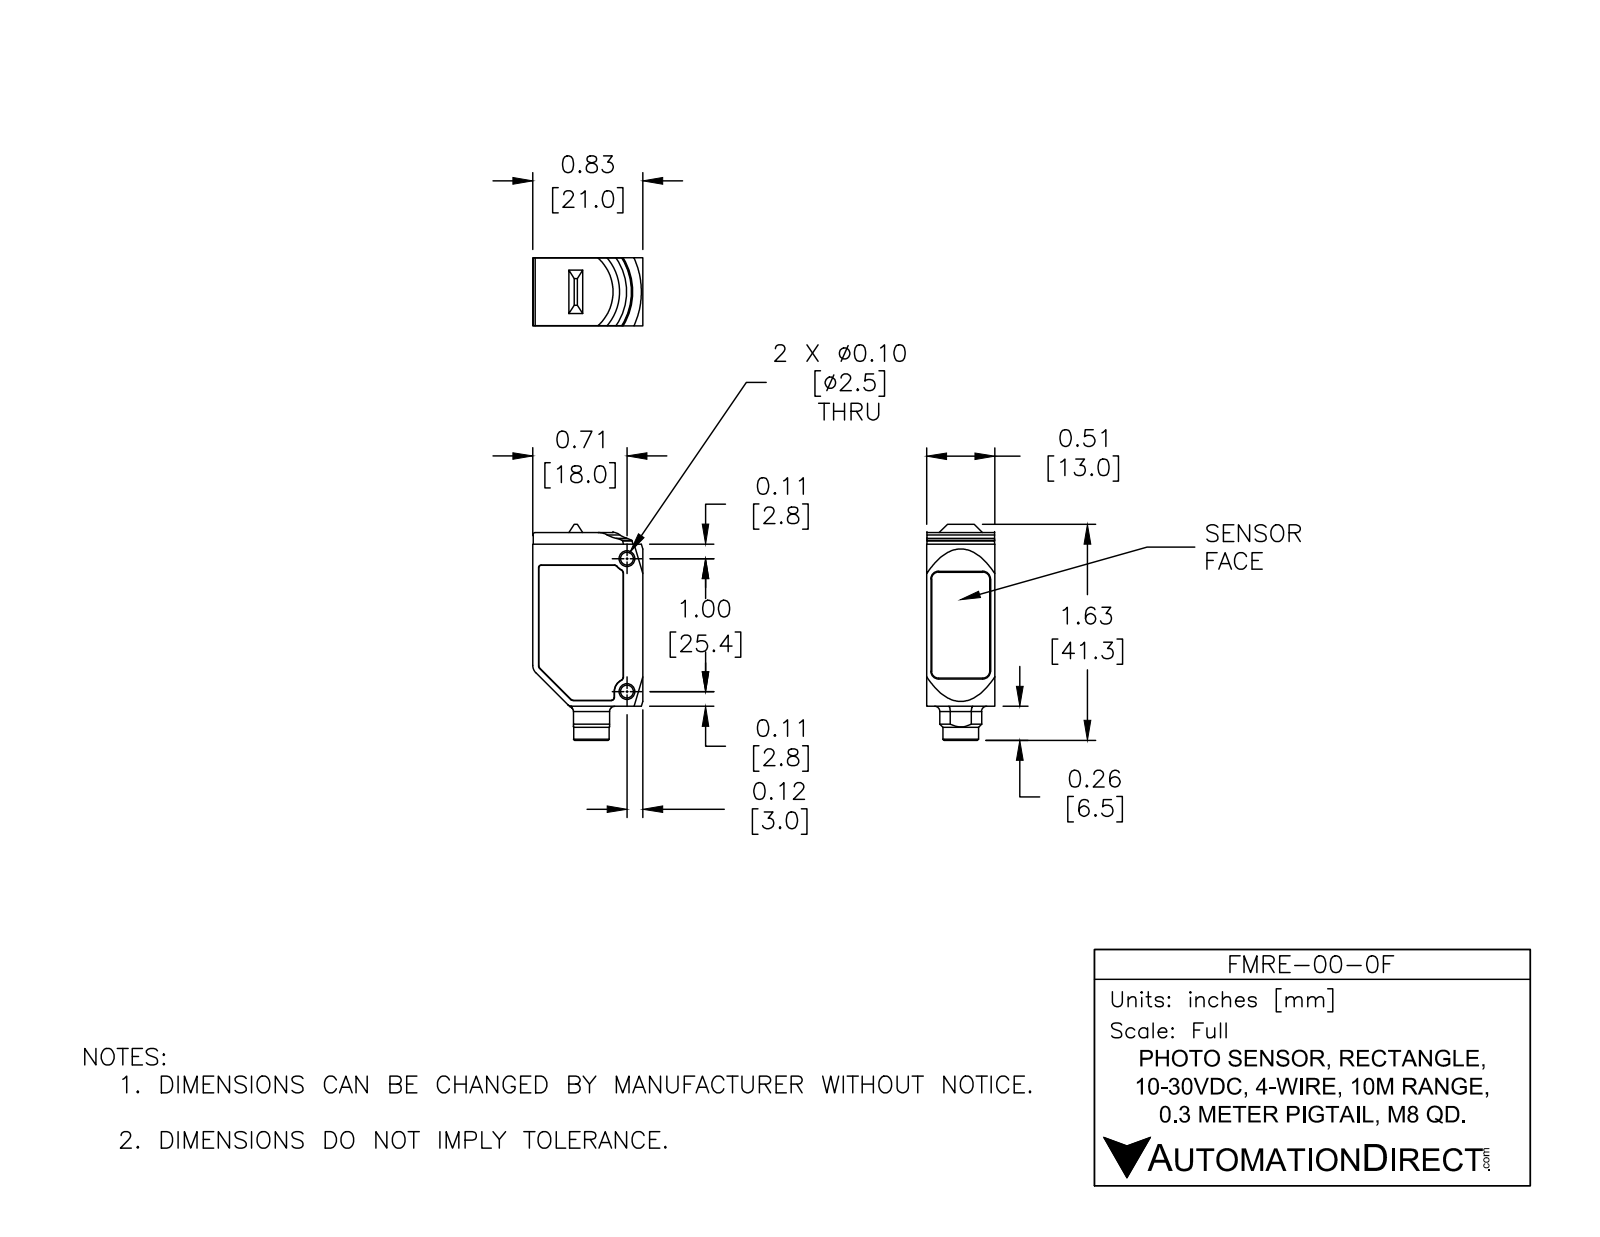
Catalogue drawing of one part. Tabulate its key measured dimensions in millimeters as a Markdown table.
| quantity | value |
| --- | --- |
| part name | FMRE-00-0F |
| STEP written by | SolidWorks 2017 (AUTOMOTIVE_DESIGN) |
| units | millimeters |
| bodies | 1 solid, 115 faces (44 planar, 46 cylindrical, 25 other) |
| overall size | 41.3 × 21 × 13 |
| volume | 8 620 mm³ |
| surface area | 3 304 mm² |
| round holes (diameter × count) | 2.5 × 2, 5.8 × 1 |
| round bosses / shafts (diameter × count) | 6.8 × 1 |
| partial cylindrical surfaces (radius × count) | 0.5 × 7, 0.5 × 7, 1.3 × 4, 1.5 × 4, 1 × 3, 2.4 × 2, 2.4 × 2, 16.5 × 2 |
| main face-to-face distances | 13, 21, 33.2, 13, 0.9, 0.9, 0.8, 12, 12.2, 0.8 |
| hole center spacings | 25.4 |
